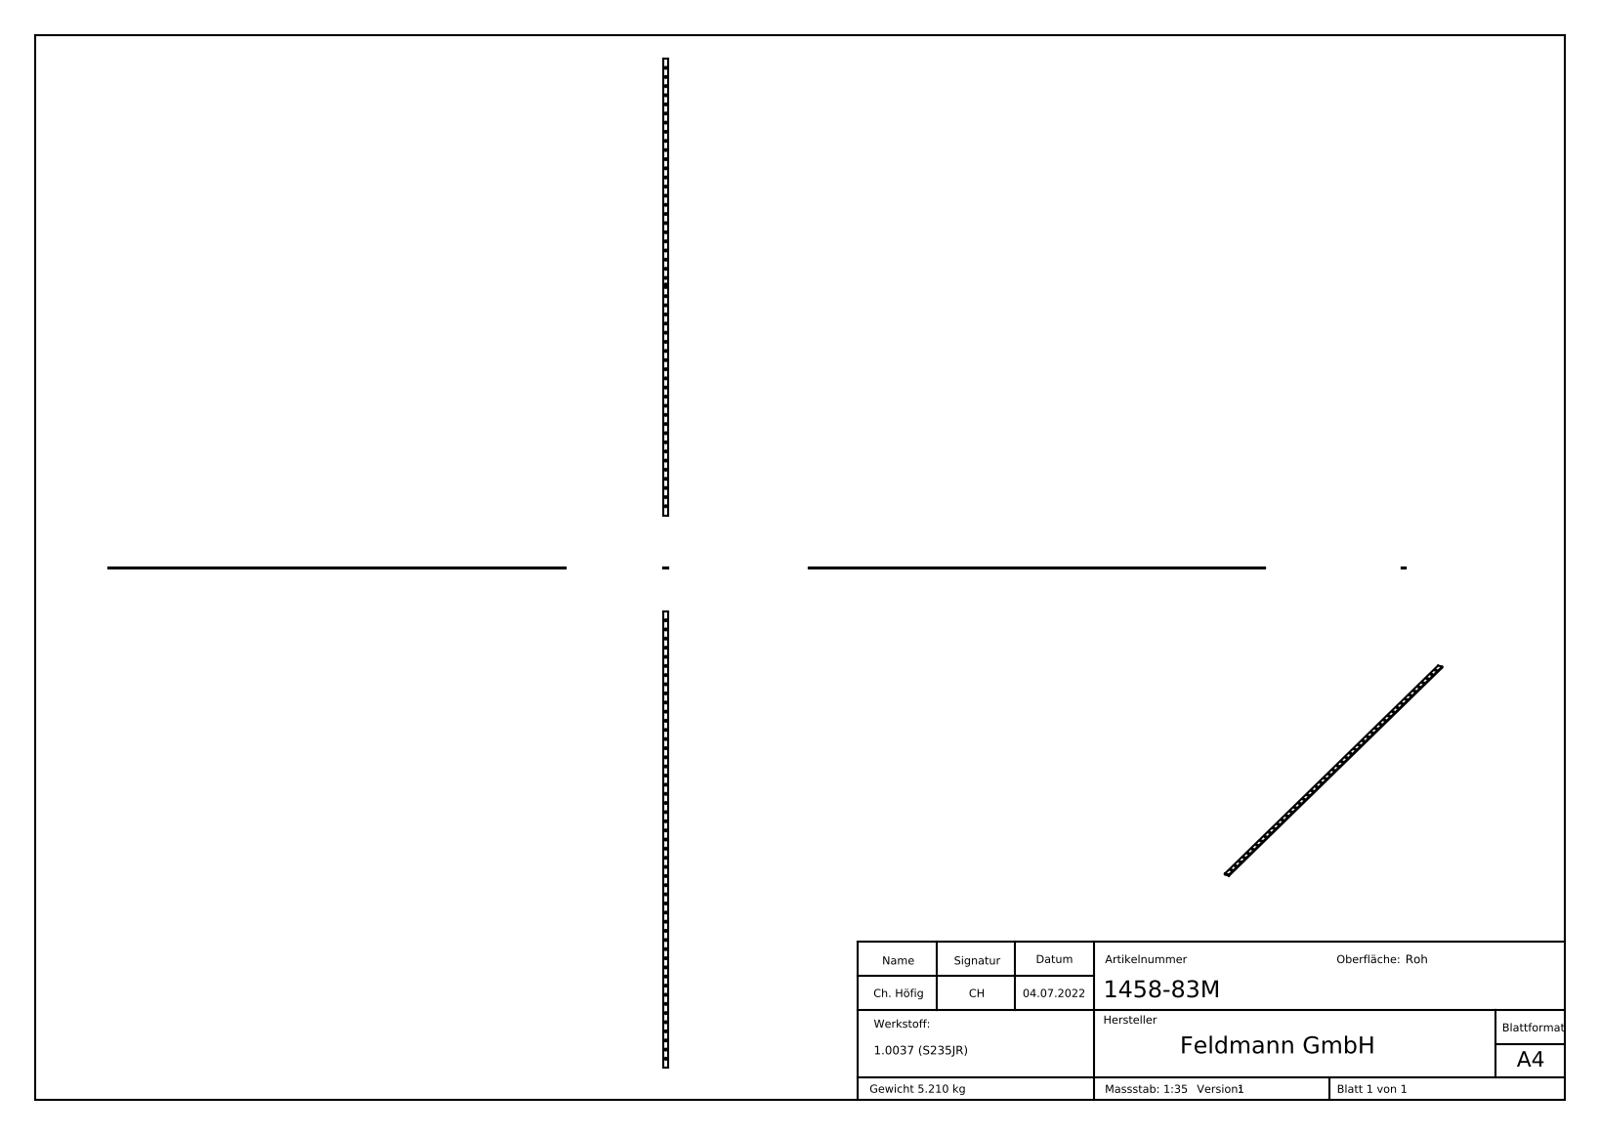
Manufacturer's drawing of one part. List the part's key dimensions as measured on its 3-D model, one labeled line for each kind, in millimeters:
Part name (STEP PRODUCT): 1458-83M
STEP written by: SolidWorks 2018 (CONFIG_CONTROL_DESIGN)
Units: millimetres
Bodies: 1 solid, 325 faces (152 planar, 49 cylindrical, 124 other)
Overall size (bounding box): 3000 × 30 × 8
Volume: 667 968 mm³ · Surface area: 231 494 mm²
Round holes (diameter × count): ⌀13 ×49
Main face-to-face distances: 8, 30, 3000, 7.9, 15, 4.46, 4.6, 0.54, 3.34, 3.07
Hole centre spacings: 60, 120, 180, 240, 300, 360, 420, 480
